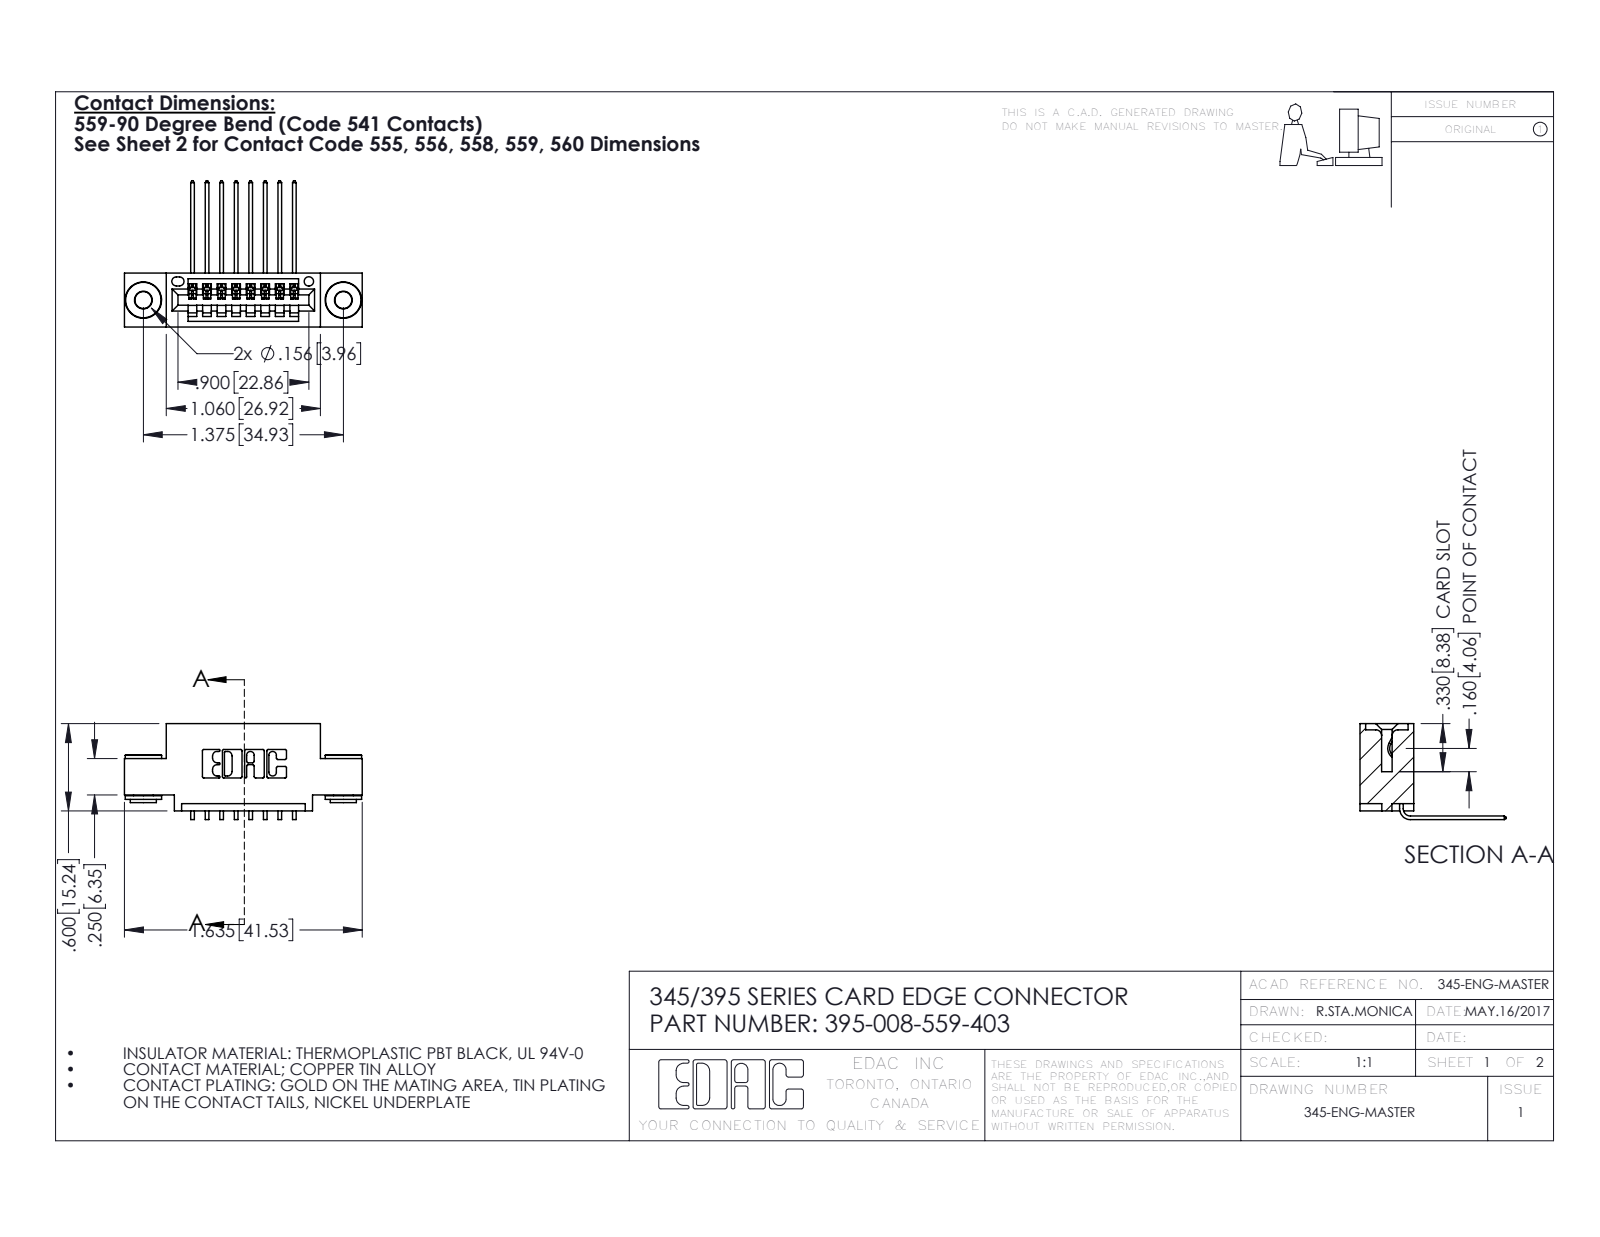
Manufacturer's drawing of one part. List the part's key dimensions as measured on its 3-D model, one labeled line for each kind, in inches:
Part name (STEP PRODUCT): 395-008-559-403; 345-292-001_558 559 Tail - 1; 345-250-002_345-250-002-102; 345 Part_0.110 Offset - 0.156 Dia-TH
STEP written by: SolidWorks 2016 (CONFIG_CONTROL_DESIGN)
Units: inches
Bodies: 11 solids, 648 faces (430 planar, 210 cylindrical, 8 other)
Overall size (bounding box): 1.635 × 1.005 × 0.659
Volume: 0.222 in³ · Surface area: 7.481 in²
Round holes (diameter × count): ⌀0.116 ×2, ⌀0.156 ×2, ⌀0.064 ×1
Round bosses / shafts (diameter × count): ⌀0.25 ×2, ⌀0.18 ×2, ⌀0.136 ×2
Partial cylindrical surfaces — rounded edges, fillets, slot ends (radius × count): R0.01 ×22, R0.006 ×16, R0.007 ×6, R0.031 ×6, R0.026 ×3, R0.031 ×2, R0.04 ×2, R0.014 ×1
Main face-to-face distances: 0.2, 0.37, 0.1, 0.072, 0.298, 0.3, 0.025, 0.16, 0.06, 0.4
Hole centre spacings: 0.27, 1.144, 1.375
